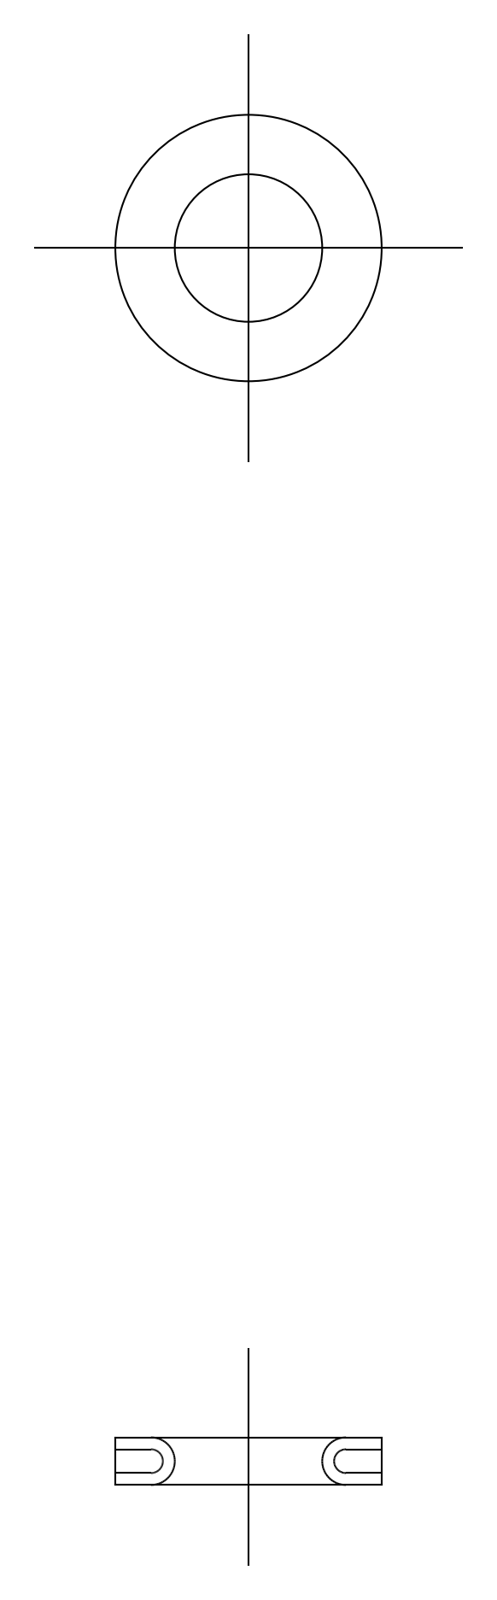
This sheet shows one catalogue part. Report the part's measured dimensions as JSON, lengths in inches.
{"part_name": "grommet", "step_written_by": "CADfix (AUTOMOTIVE_DESIGN)", "units": "inches", "bodies": {"solids": 1, "faces": 12, "planar": 0, "cylindrical": 0, "other": 12}, "overall_size": [0.441, 0.441, 0.079], "volume_in3": 0.004, "surface_area_in2": 0.502}
